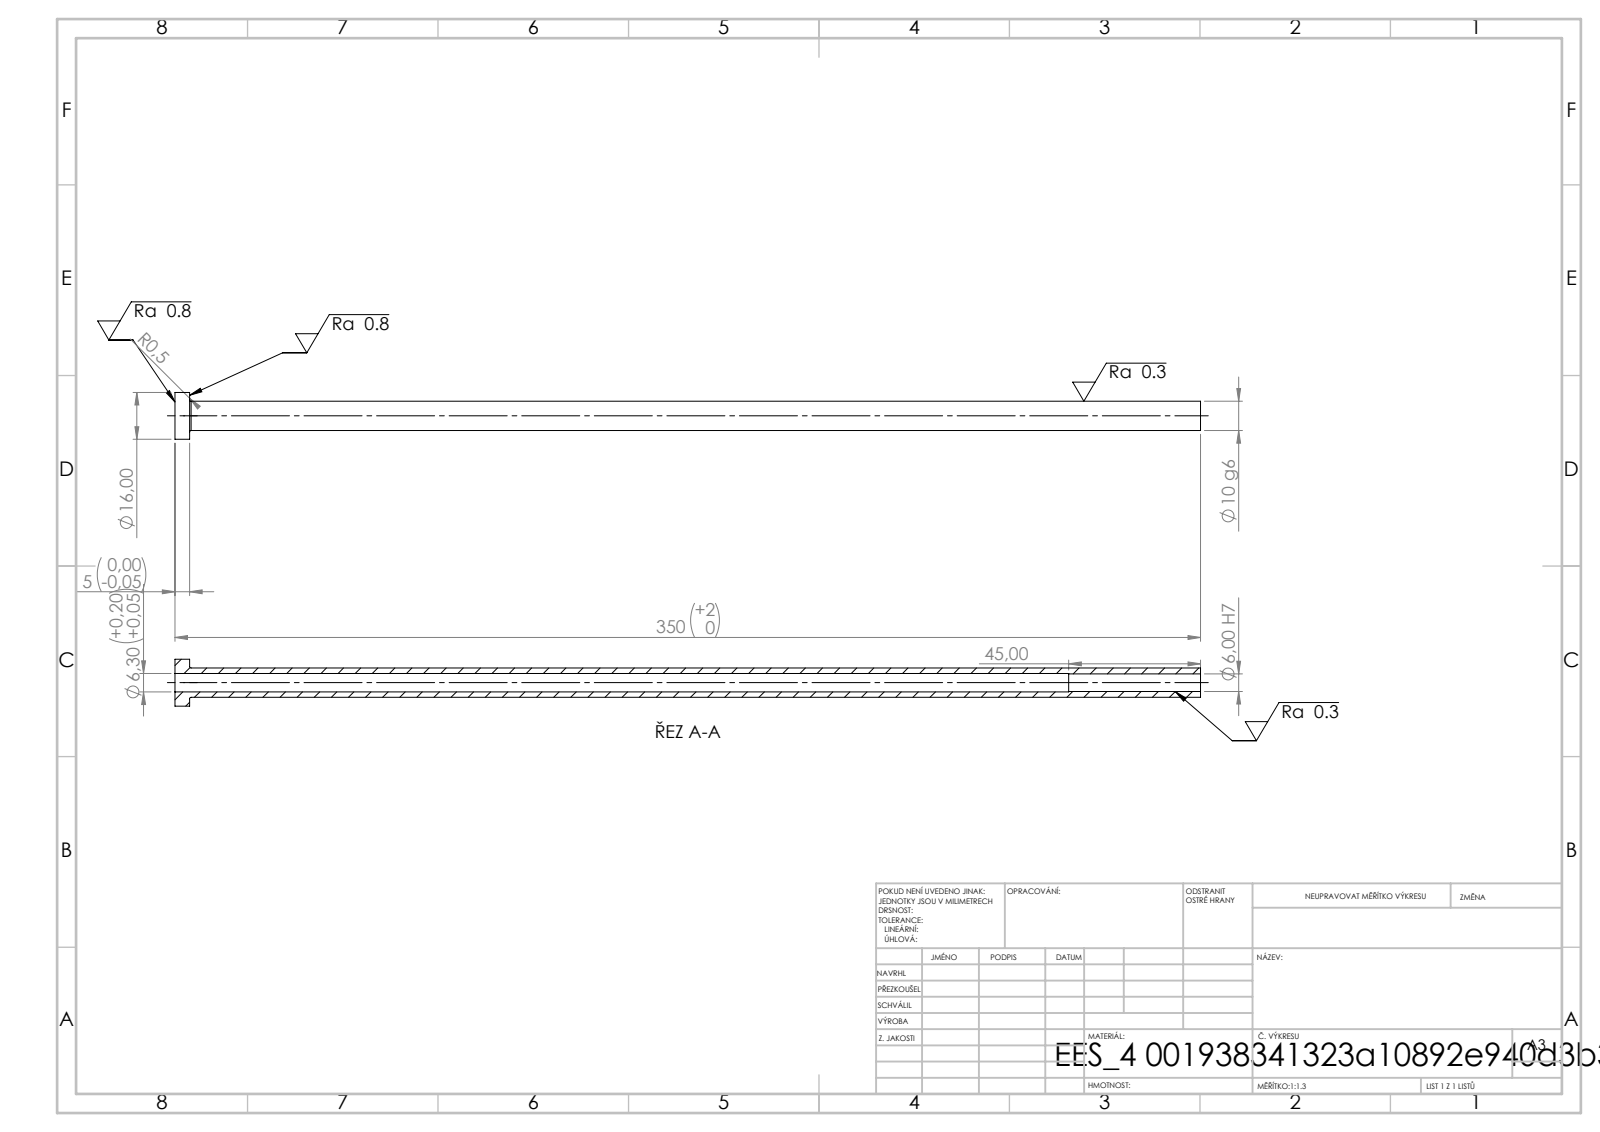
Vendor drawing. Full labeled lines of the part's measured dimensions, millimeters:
STEP written by: SolidWorks 2019 (CONFIG_CONTROL_DESIGN)
Units: millimetres
Bodies: 1 solid, 14 faces (4 planar, 8 cylindrical, 2 other)
Overall size (bounding box): 350 × 16 × 16
Volume: 17 323 mm³ · Surface area: 18 314 mm²
Round holes (diameter × count): ⌀6 ×1, ⌀6.3 ×1
Round bosses / shafts (diameter × count): ⌀16 ×1, ⌀10 ×1
Main face-to-face distances: 5, 350, 345, 305, 300, 45
